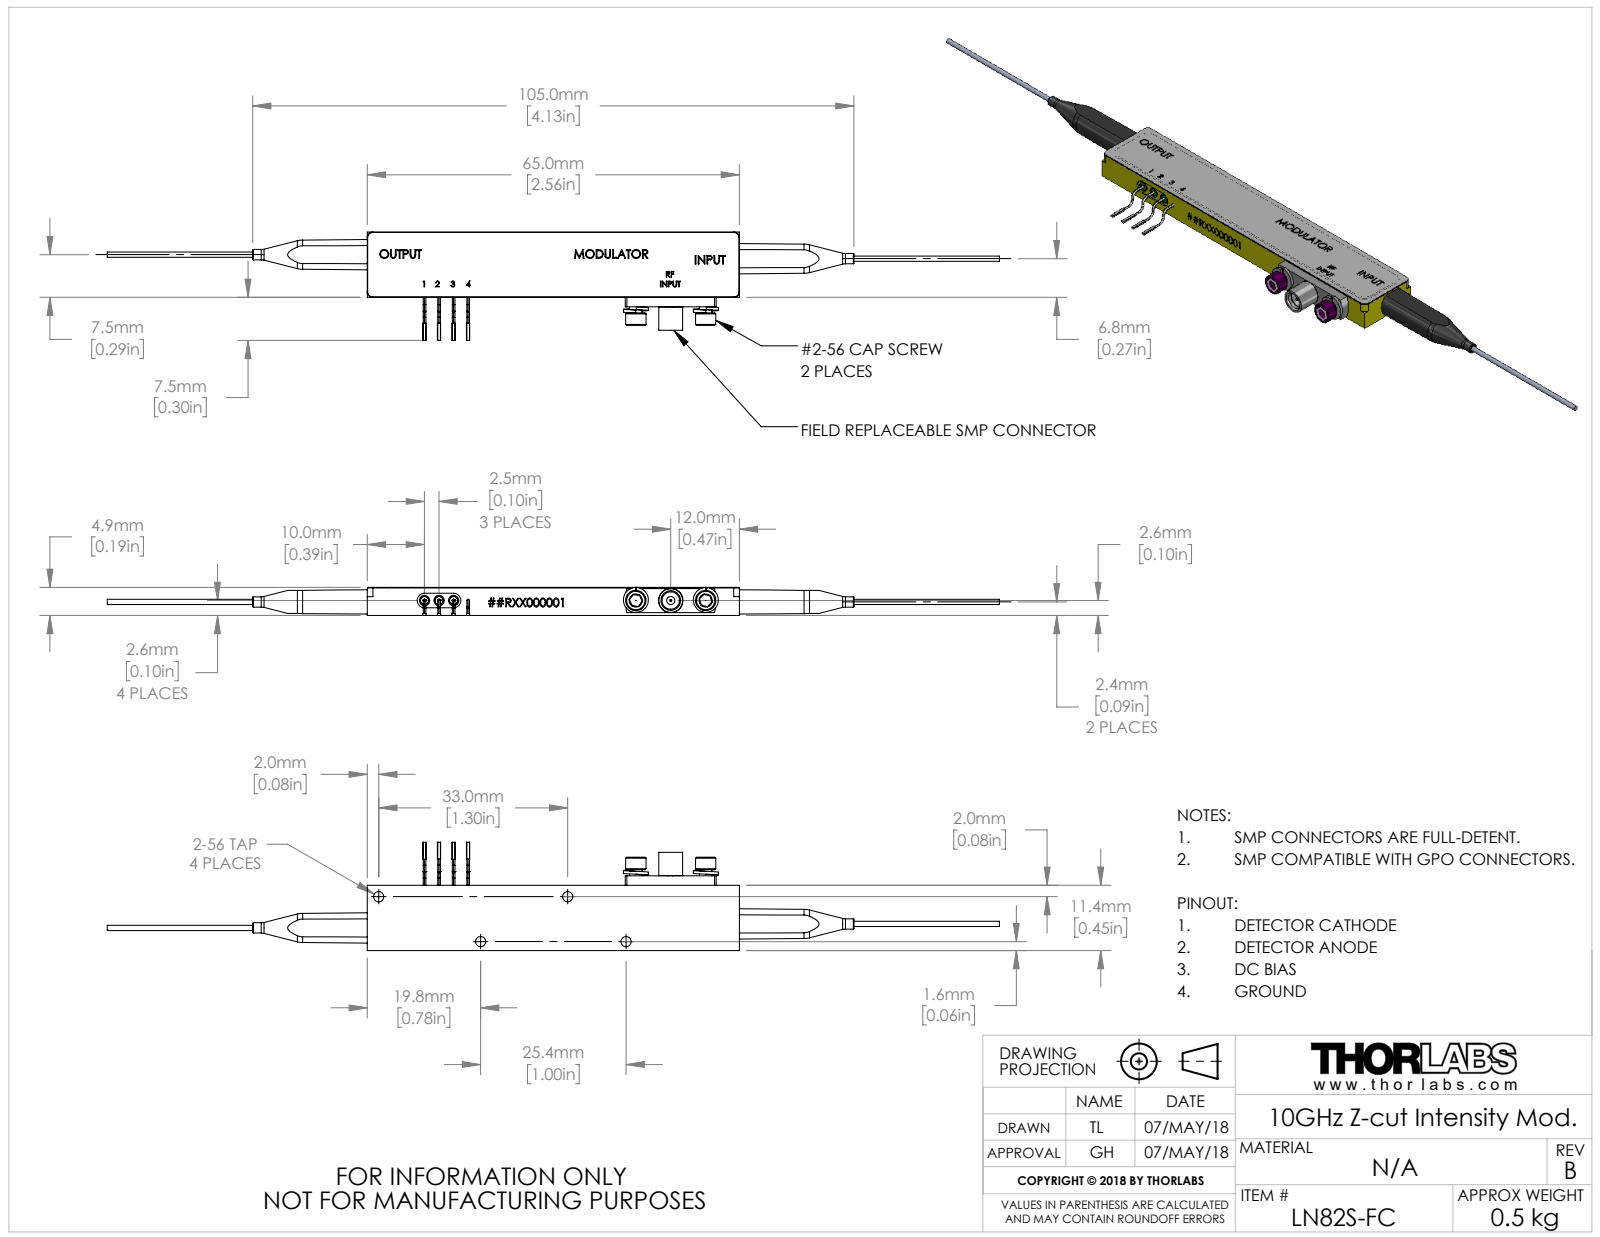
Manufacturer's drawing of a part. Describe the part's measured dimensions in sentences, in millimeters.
The part is named "20761-E0W". Its 3-D file was written by "SolidWorks 2016 (CONFIG_CONTROL_DESIGN)". It is 0 solids with 458 faces: 211 planar, 115 cylindrical and 132 other. Overall it measures 155.8 by 18.89 by 4.91 millimeters. Round holes: 4 of diameter 1.78, 3 of diameter 1.8, 1 of diameter 2.61, 1 of diameter 3.05, 1 of diameter 3.18. Round bosses or shafts: 4 of diameter 0.46, 2 of diameter 3.56, 2 of diameter 2.18, 2 of diameter 1.8, 2 of diameter 0.9, 1 of diameter 4.16, 1 of diameter 1.45, 1 of diameter 0.38. Partial cylindrical surfaces (rounded edges, fillets, slot ends): 12 of radius 0.23, 4 of radius 0.9, 4 of radius 1, 2 of radius 1.27, 1 of radius 7.93. The main face-to-face distances are 4.91, 11.4, 4.78, 4.83, 65, 1.65, 13.05, 0.5, 4.7, 4.2. The hole center spacings are 2.54, 5.08, 6.1, 12.86, 17.1, 19.45, 25.4, 33.
